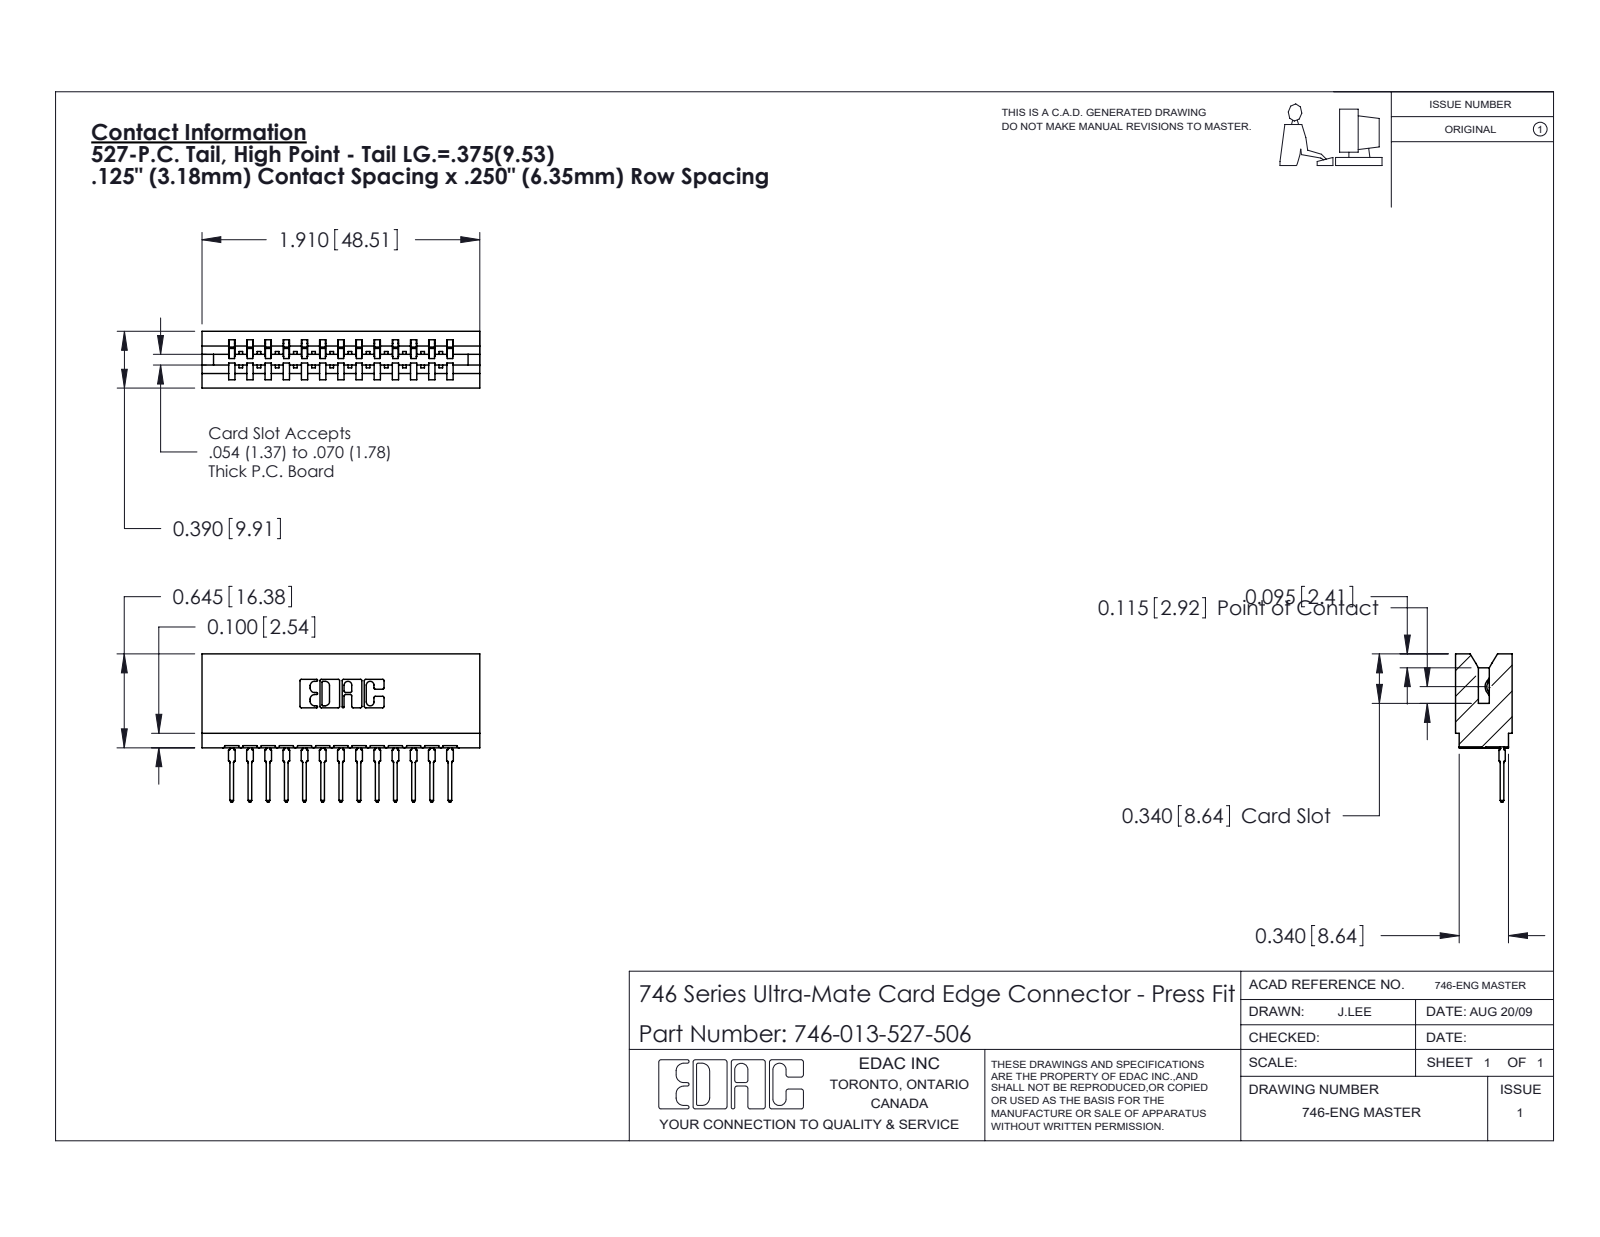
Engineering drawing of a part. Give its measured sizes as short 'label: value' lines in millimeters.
name: 746 Part_.340 Slot Depth - 06; 746-292-001_527; 746-013-527-506
written by: SolidWorks 2020 (CONFIG_CONTROL_DESIGN)
unit: mm
bodies: 14 solids, 1502 faces (875 planar, 289 cylindrical, 338 other)
size: 48.5 × 25.9 × 9.9
volume: 5 620 mm³; area: 7 213 mm²
rounds: 26× R0.5, 22× R0.3, 14× R0.4, 6× R0.2, 6× R0.8, 4× R0.1, 4× R0.3, 3× R0.7
face distances: 6.4, 12.7, 8.5, 1.4, 3.2, 9.9, 7.4, 13.8, 19.1, 3.2
